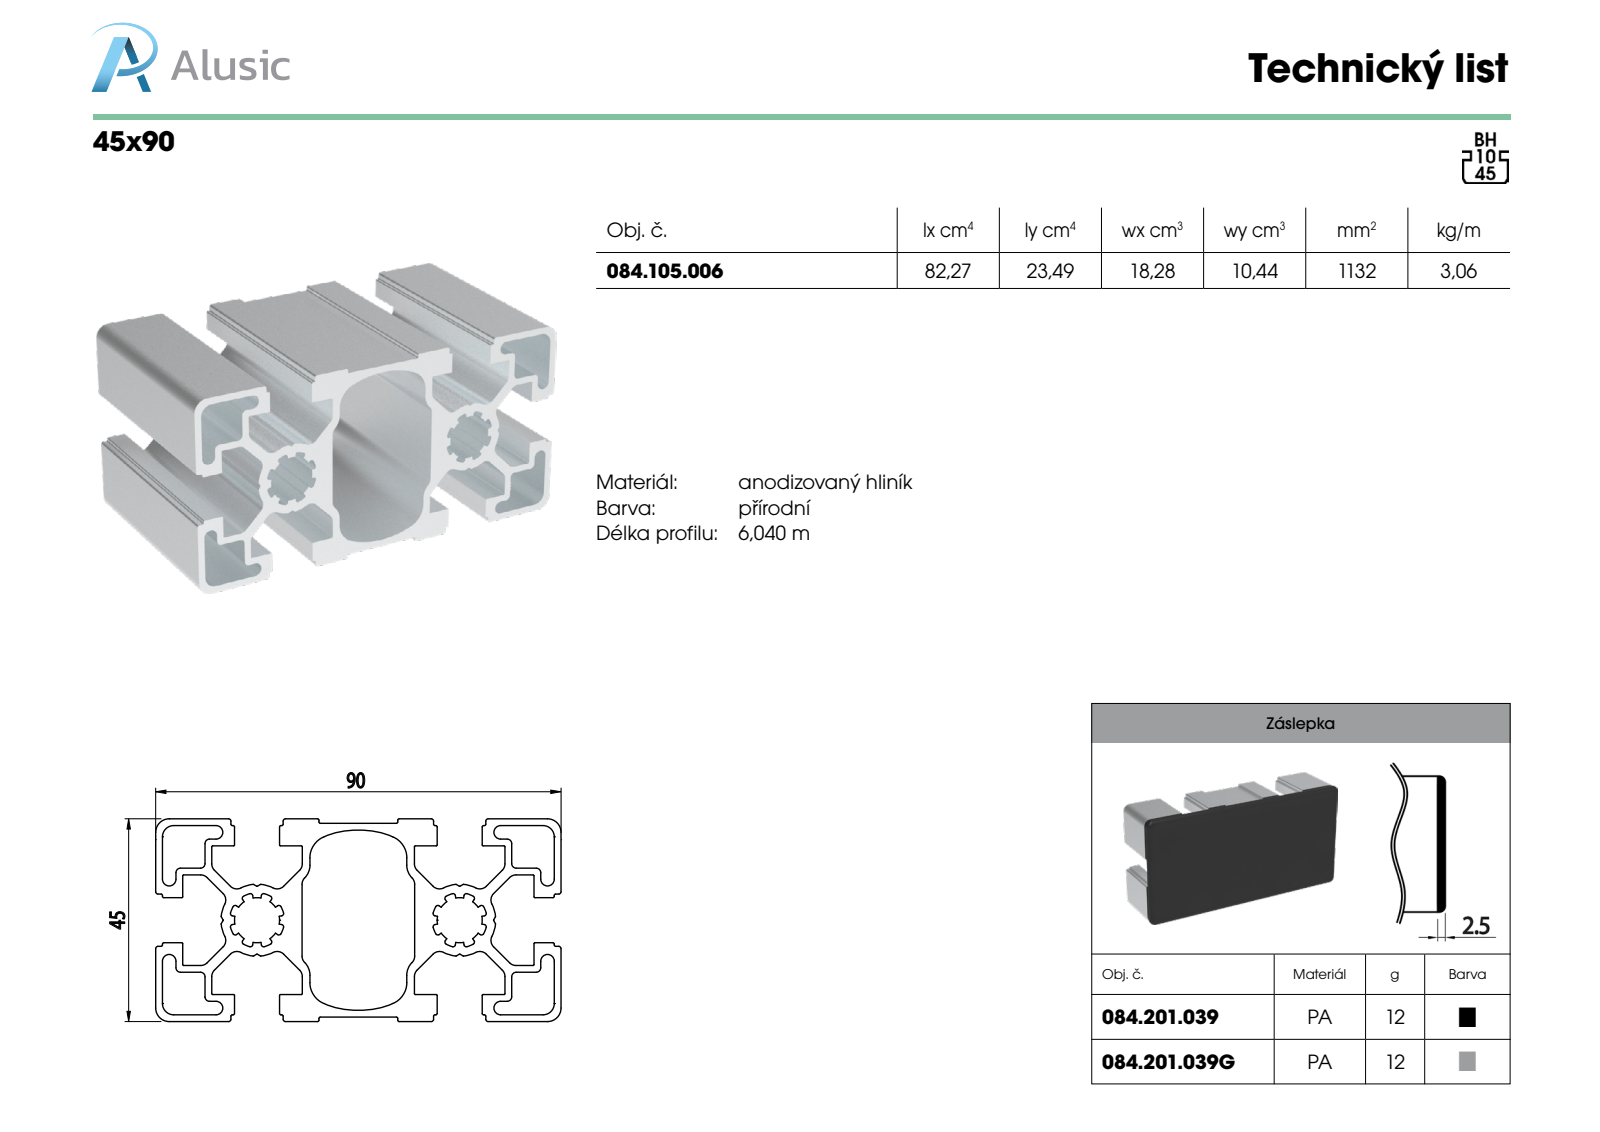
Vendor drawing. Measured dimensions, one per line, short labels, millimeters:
name: 084.105.006
written by: SolidWorks 2018 (AUTOMOTIVE_DESIGN)
unit: mm
bodies: 1 solid, 430 faces (175 planar, 255 cylindrical, 0 other)
size: 100 × 90 × 45
volume: 113 187 mm³; area: 96 439 mm²
rounds: 44× R0.5, 42× R0.2, 32× R0.3, 28× R2, 12× R1, 8× R1.5, 6× R5, 4× R2.5
face distances: 1.5, 45, 10.95, 4.5, 6, 5, 32.55, 5.05, 15.05, 39
